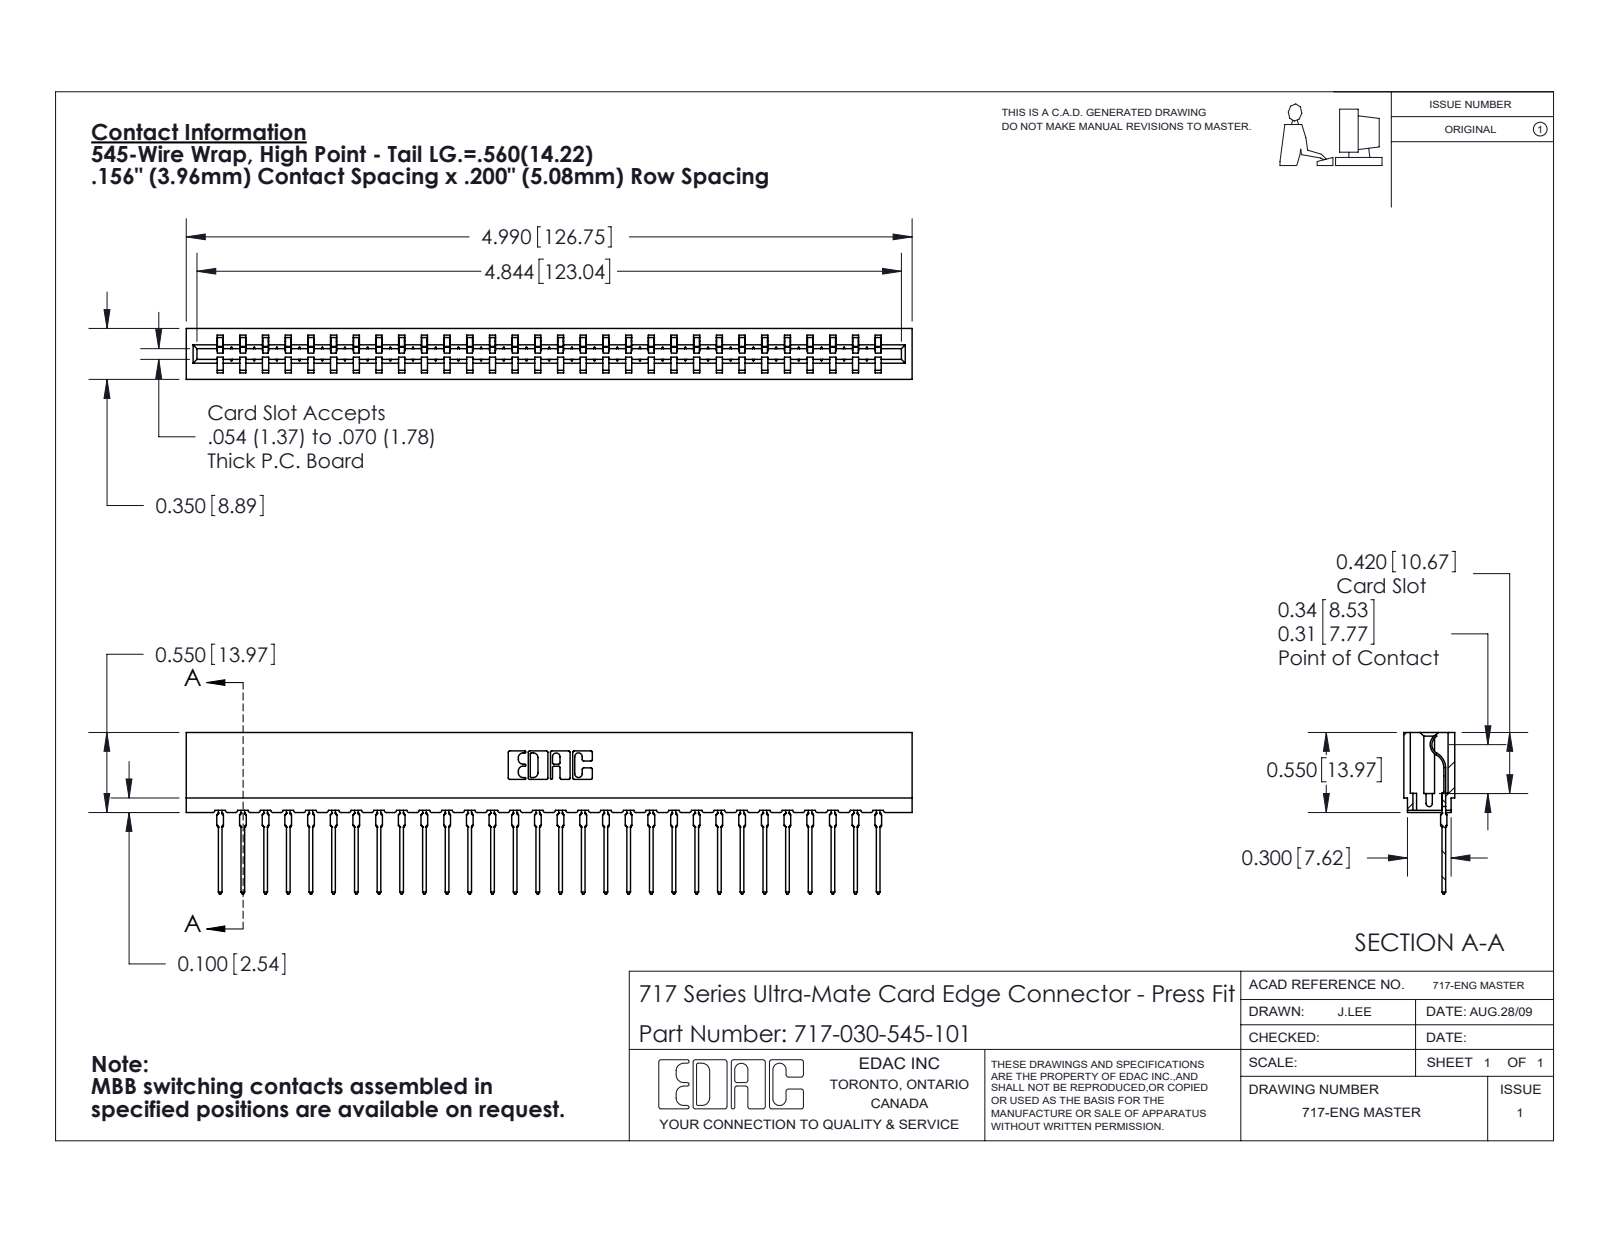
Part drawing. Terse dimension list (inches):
name: 717-030-545-101; 745-292-001_545; 717 Part_Insulator Option - 06
written by: SolidWorks 2020 (CONFIG_CONTROL_DESIGN)
unit: in
bodies: 31 solids, 3484 faces (2094 planar, 610 cylindrical, 780 other)
size: 4.99 × 1.109 × 0.35
volume: 0.662 in³; area: 24.13 in²
rounds: 60× R0.015, 60× R0.021, 22× R0.01, 6× R0.007, 6× R0.031, 4× R0.005, 4× R0.011, 3× R0.026
face distances: 0.212, 0.138, 0.35, 0.074, 0.063, 0.287, 0.076, 0.149, 0.156, 0.045
